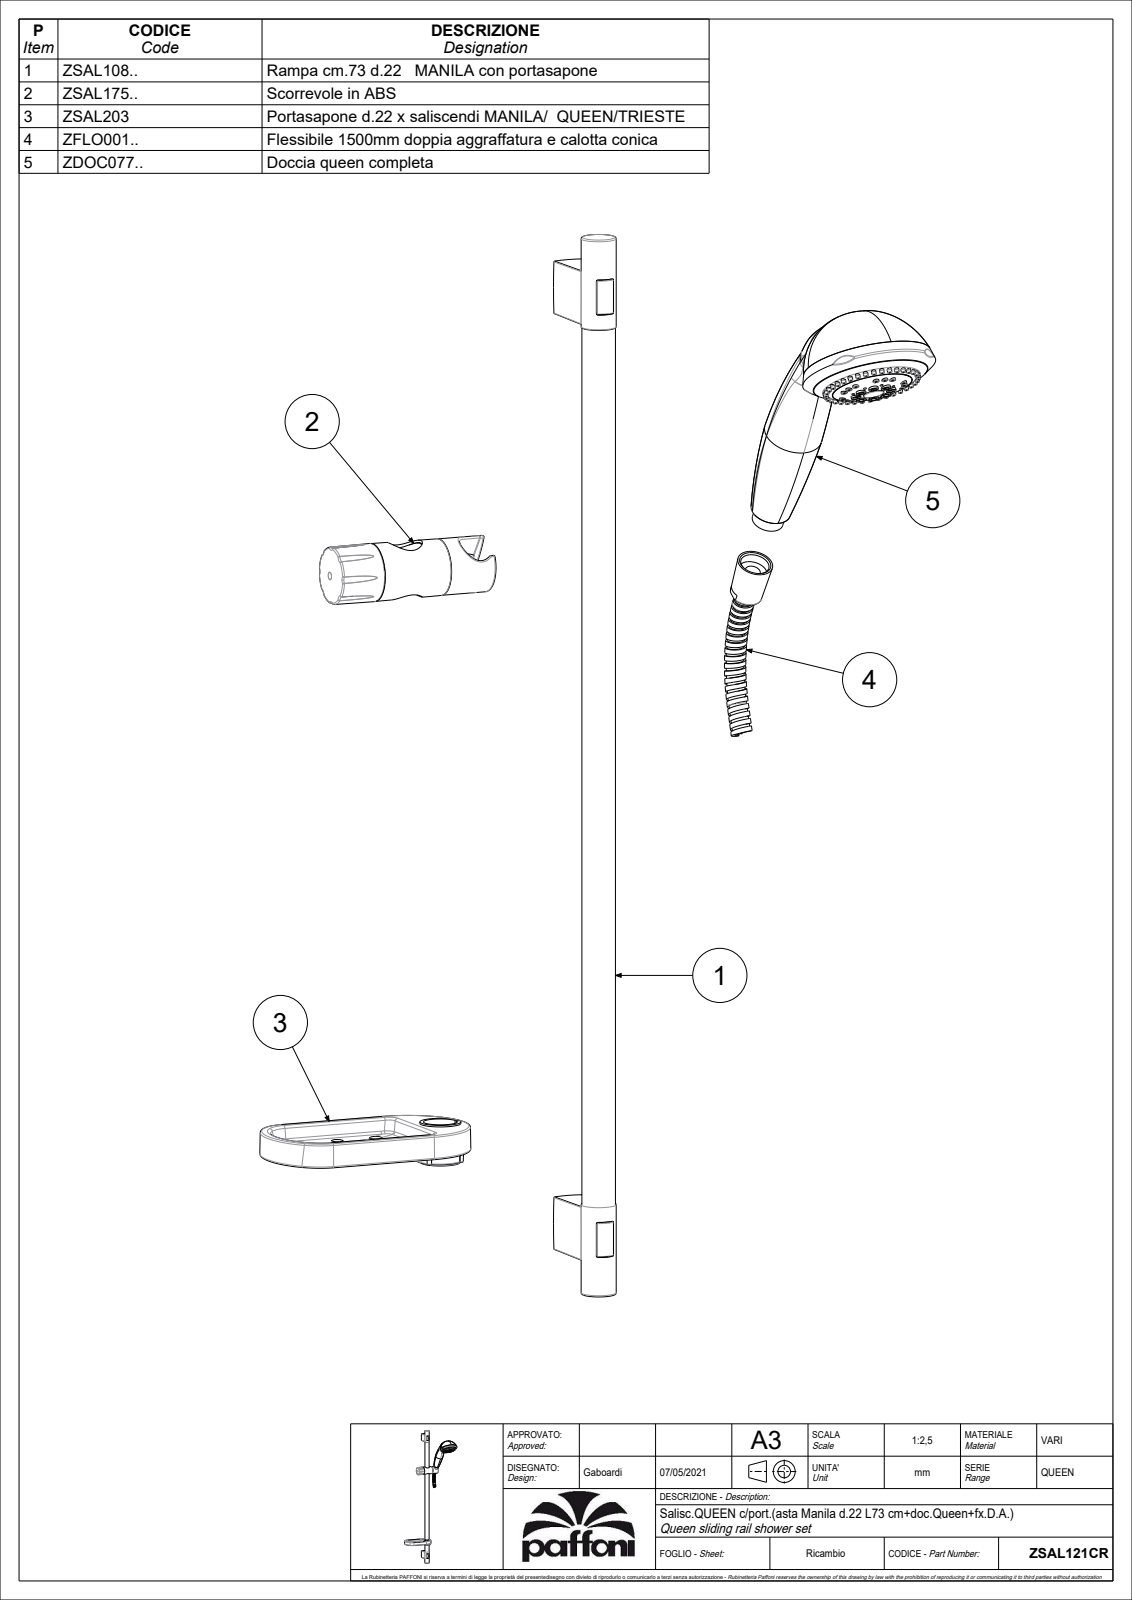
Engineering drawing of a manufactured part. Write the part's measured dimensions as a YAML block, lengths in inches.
part_name: "ZSAL121CR"
step_written_by: "CREO PARAMETRIC BY PTC INC, 2020044 (CONFIG_CONTROL_DESIGN)"
units: inches
bodies: {solids: 8, faces: 1797, planar: 402, cylindrical: 489, other: 906}
overall_size: [27.795, 9.99, 8.508]
volume: 34.61
surface_area: 400.6
round_holes:
  - {diameter: 0.031, count: 36}
  - {diameter: 0.059, count: 15}
  - {diameter: 0.079, count: 8}
  - {diameter: 0.157, count: 8}
  - {diameter: 0.366, count: 1}
  - {diameter: 0.472, count: 1}
  - {diameter: 0.827, count: 1}
  - {diameter: 0.874, count: 1}
  - {diameter: 1.382, count: 1}
  - {diameter: 2.106, count: 1}
round_bosses_or_shafts:
  - {diameter: 0.248, count: 8}
  - {diameter: 0.118, count: 8}
  - {diameter: 2.047, count: 1}
  - {diameter: 1.461, count: 1}
  - {diameter: 1.303, count: 1}
  - {diameter: 1.264, count: 1}
  - {diameter: 1.252, count: 1}
  - {diameter: 1.173, count: 1}
partial_cylinders:
  - {radius: 0.039, count: 54}
  - {radius: 0.059, count: 41}
  - {radius: 0.02, count: 20}
  - {radius: 0.079, count: 19}
  - {radius: 0.031, count: 4}
  - {radius: 0.053, count: 4}
  - {radius: 0.056, count: 4}
  - {radius: 0.073, count: 4}
face_to_face_distances: [0.492, 0.079, 0.098, 0.394, 0.531, 0.138, 0.63, 0.039, 0.059, 0.404]
hole_center_spacings: [0.861, 0.581, 0.827, 1.014, 0.228, 0.463, 0.571, 0.239]
